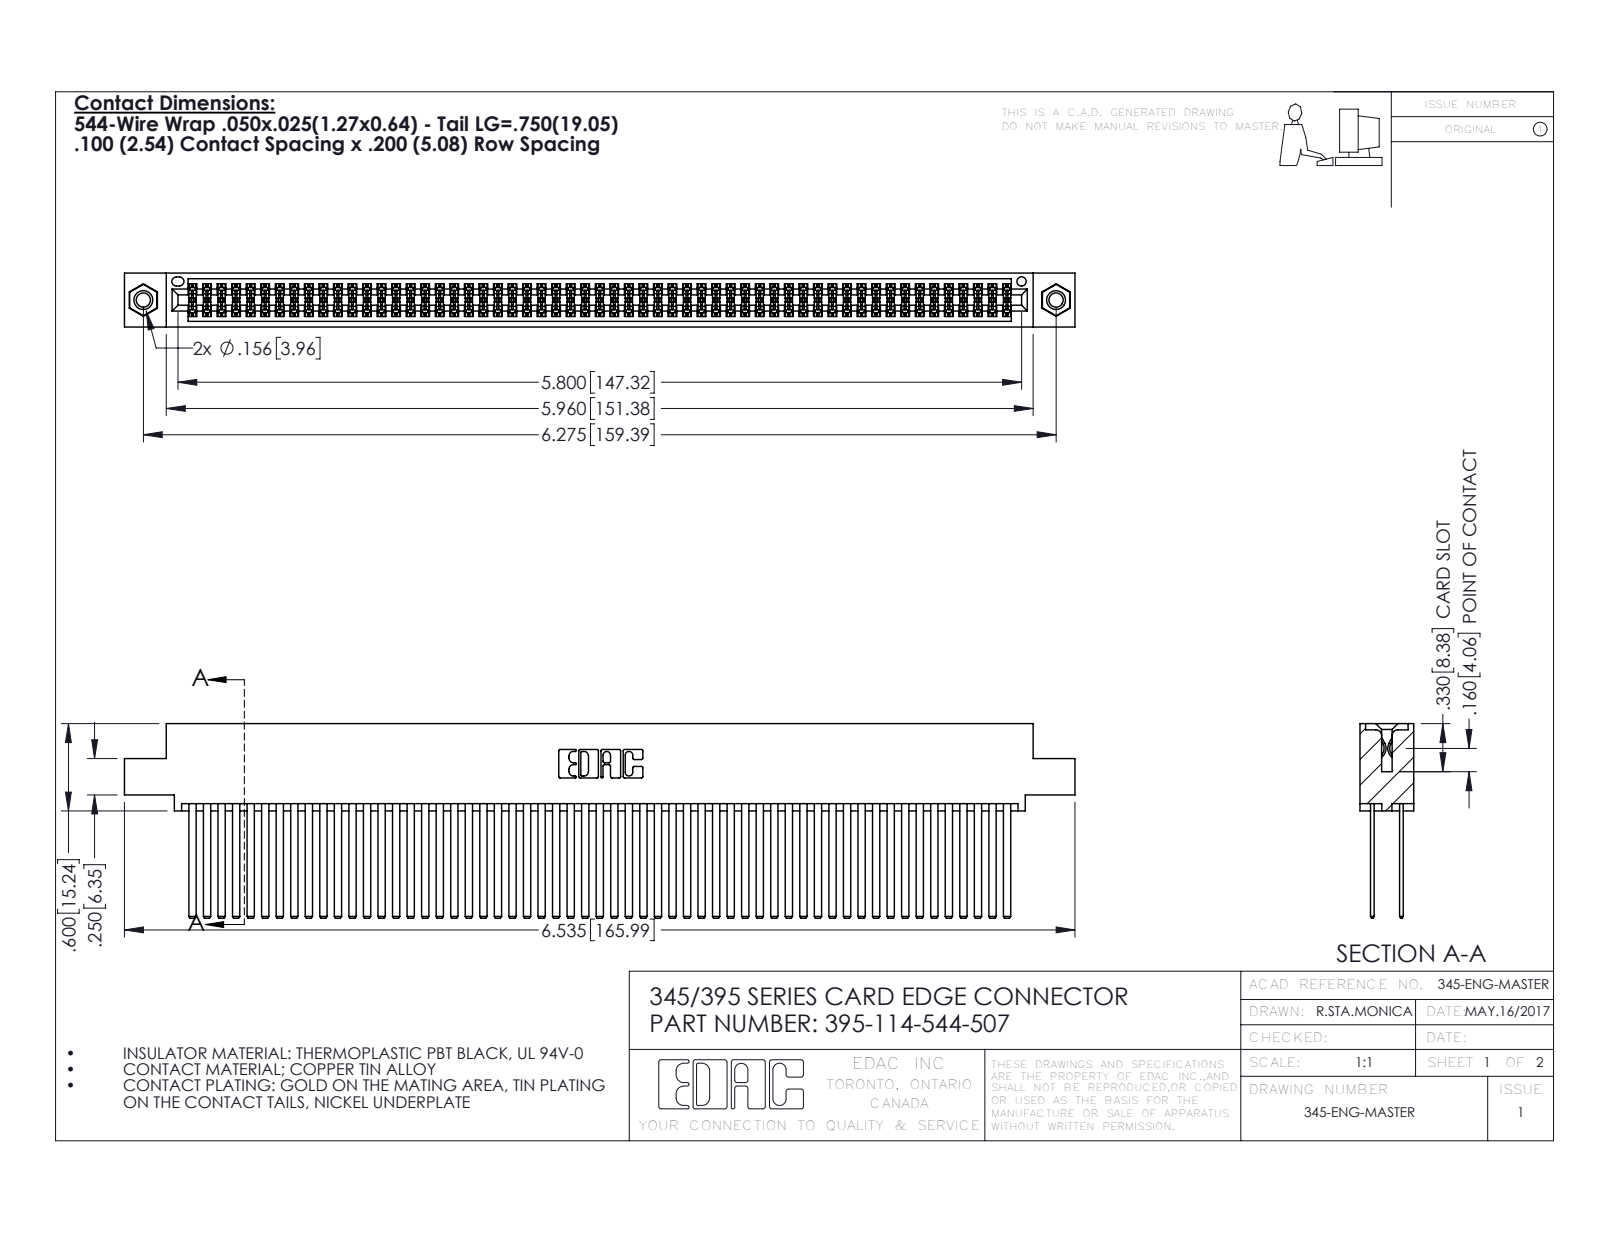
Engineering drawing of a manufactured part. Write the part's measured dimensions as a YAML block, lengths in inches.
part_name: "345-250-001_345-250-005-103; 345-292-001_345-293-144; 345 Part_0.110 Offset - 0.156 Dia-TI; 395-114-544-507"
step_written_by: "SolidWorks 2016 (CONFIG_CONTROL_DESIGN)"
units: inches
bodies: {solids: 117, faces: 5206, planar: 3422, cylindrical: 1768, other: 16}
overall_size: [6.535, 1.337, 0.37]
volume: 1.085
surface_area: 48.62
round_holes:
  - {diameter: 0.098, count: 2}
  - {diameter: 0.125, count: 2}
  - {diameter: 0.156, count: 2}
  - {diameter: 0.064, count: 1}
round_bosses_or_shafts:
  - {diameter: 0.155, count: 2}
partial_cylinders:
  - {radius: 0.006, count: 171}
  - {radius: 0.01, count: 22}
  - {radius: 0.007, count: 6}
  - {radius: 0.031, count: 6}
  - {radius: 0.026, count: 3}
  - {radius: 0.014, count: 2}
  - {radius: 0.019, count: 2}
  - {radius: 0.022, count: 2}
face_to_face_distances: [0.2, 0.025, 0.072, 0.098, 0.272, 0.298, 0.225, 0.175, 0.37, 0.05]
hole_center_spacings: [0.27, 6.039, 6.275]
